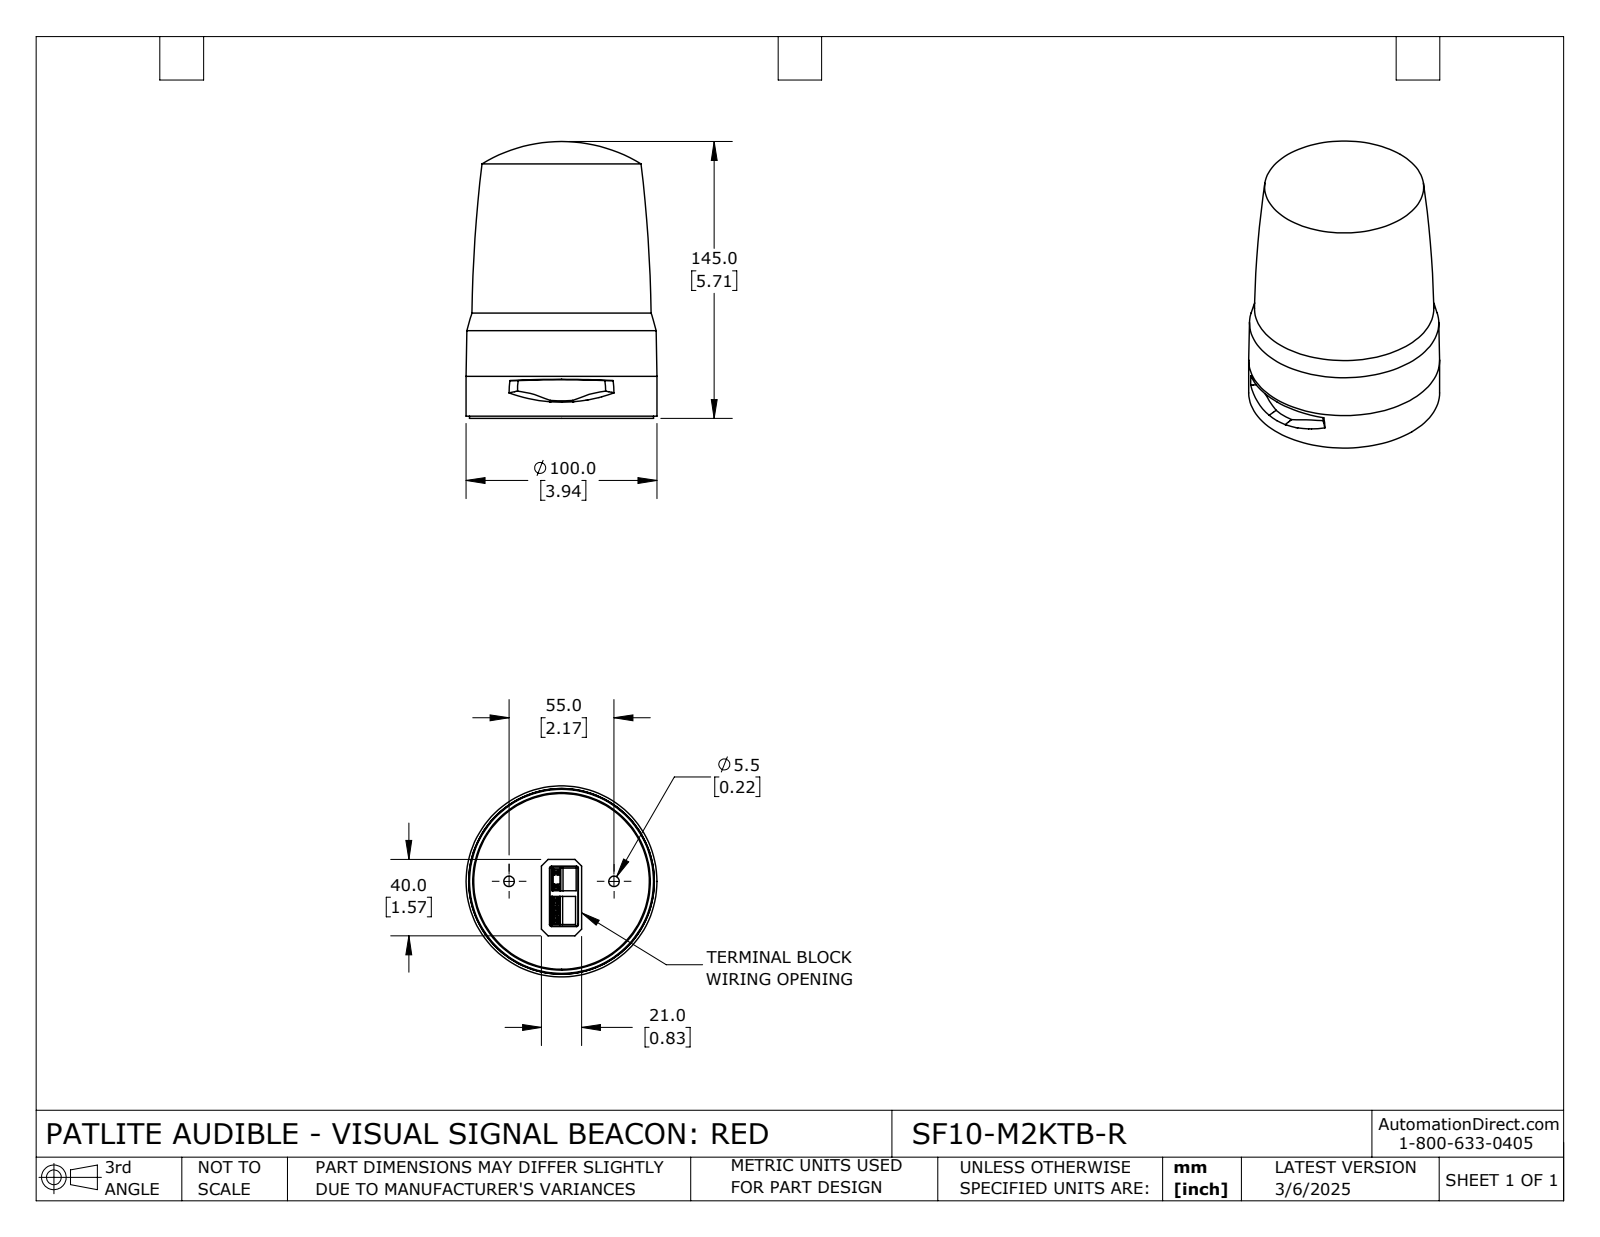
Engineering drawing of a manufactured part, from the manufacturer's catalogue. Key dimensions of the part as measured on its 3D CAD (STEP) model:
Part name (STEP PRODUCT): SF10-M2KTB-R
STEP written by: SolidWorks 2024 (CONFIG_CONTROL_DESIGN)
Units: millimetres
Bodies: 2 solids, 275 faces (174 planar, 31 cylindrical, 70 other)
Overall size (bounding box): 145 × 100 × 100
Volume: 875 277 mm³ · Surface area: 79 857 mm²
Round holes (diameter × count): ⌀5.5 ×2, ⌀13 ×2, ⌀93 ×1
Round bosses / shafts (diameter × count): ⌀100 ×1, ⌀96.4 ×1, ⌀94.5 ×1, ⌀93.2 ×1, ⌀92 ×1
Partial cylindrical surfaces — rounded edges, fillets, slot ends (radius × count): R1 ×4, R0.3 ×2, R44.75 ×1, R45 ×1
Main face-to-face distances: 6.3, 18.2, 11.9, 5.6, 12.6, 5.1, 0.4, 4.7, 1.2, 17
Hole centre spacings: 27.5, 55
